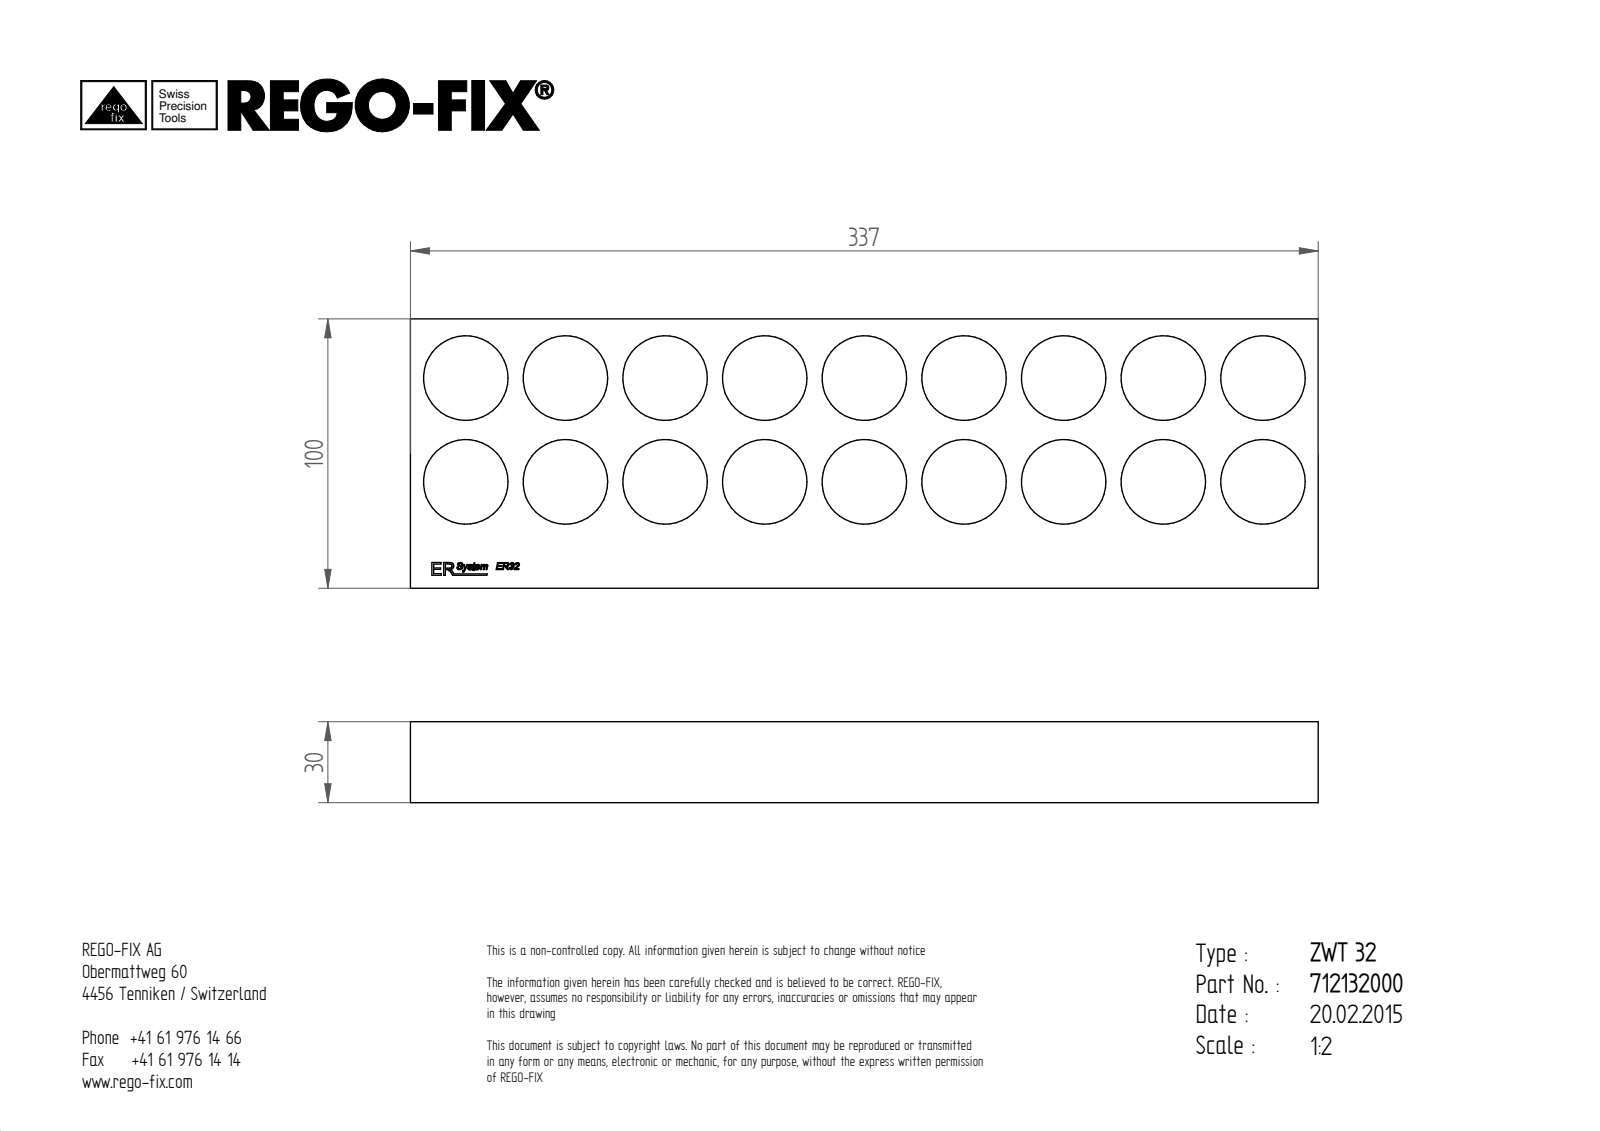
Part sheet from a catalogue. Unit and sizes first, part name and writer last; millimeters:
Units: millimetres
Overall size (bounding box): 337 × 100 × 30
Round holes (diameter × count): ⌀31.4 ×18
Main face-to-face distances: 30, 5.5, 24.5, 100, 337, 29.9, 24.4, 4.83, 95.17, 0.5
Hole centre spacings: 37, 53.4, 74, 83.42, 111, 117.49, 148, 152.93
Volume: 669 498 mm³ · Surface area: 137 142 mm²
Bodies: 1 solid, 158 faces (110 planar, 18 cylindrical, 30 other)
STEP written by: Unknown (AUTOMOTIVE_DESIGN)
